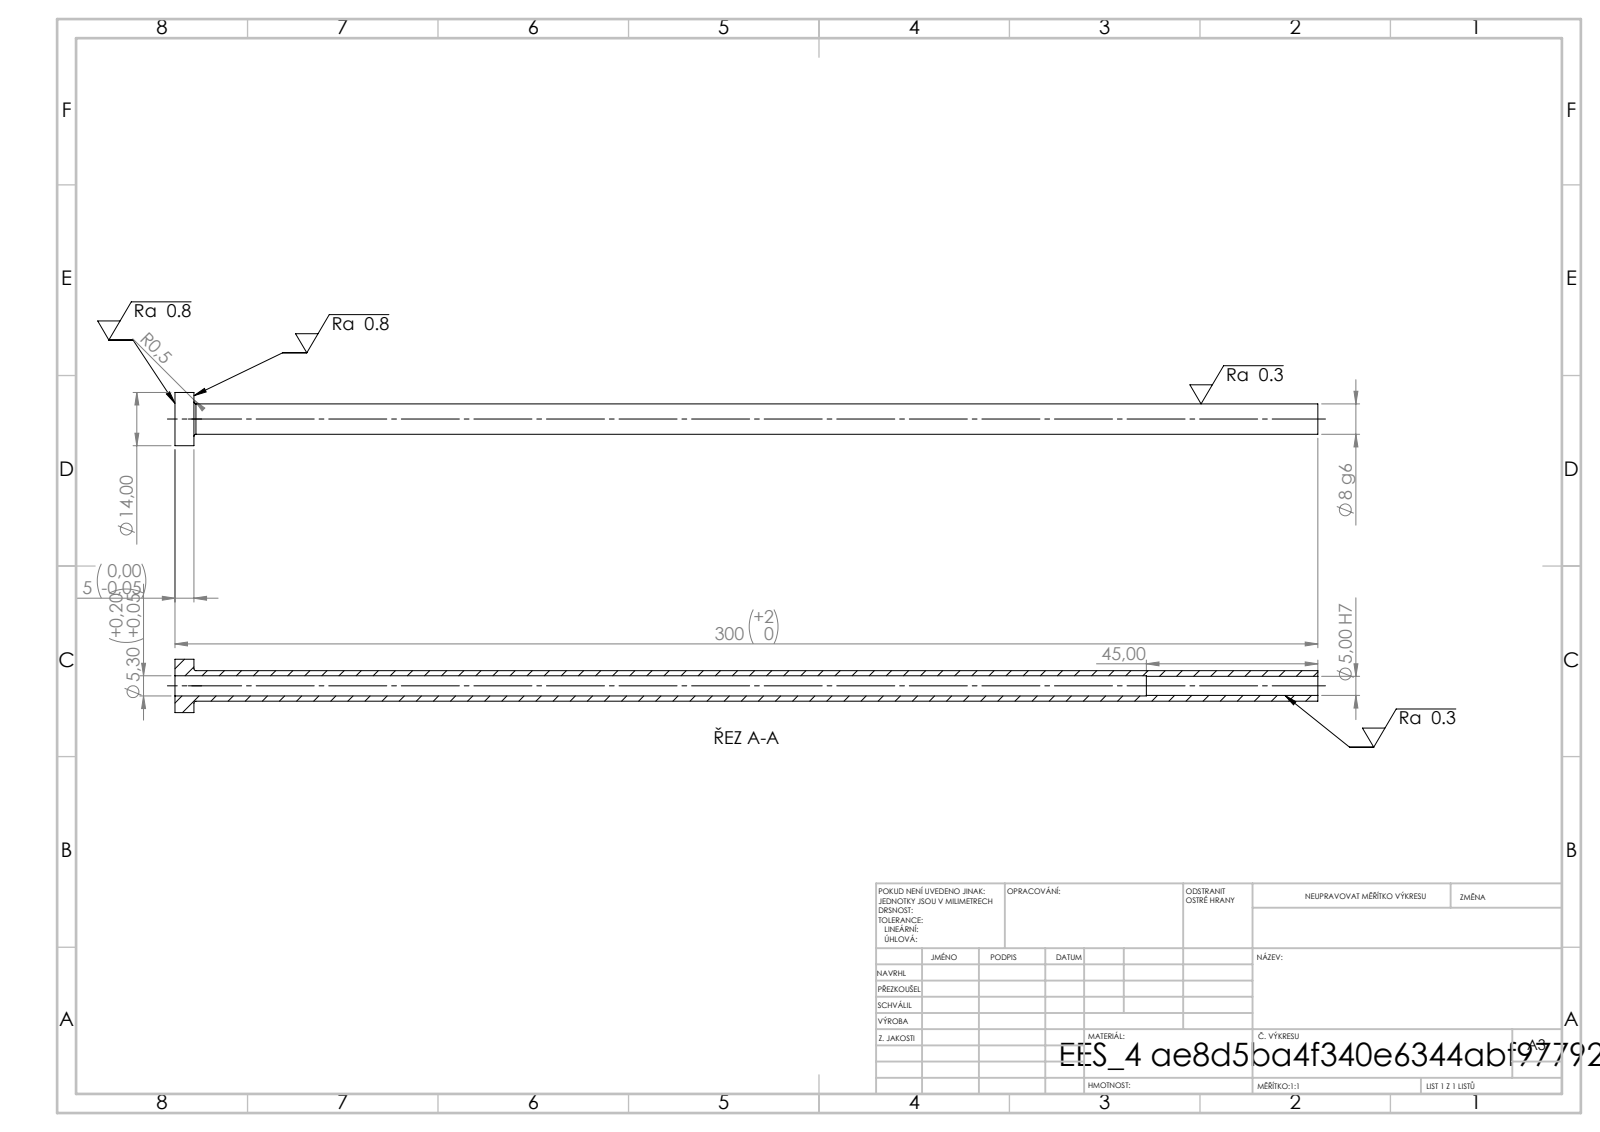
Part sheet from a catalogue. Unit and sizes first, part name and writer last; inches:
Units: inches
Overall size (bounding box): 11.811 × 0.551 × 0.551
Round holes (diameter × count): ⌀0.197 ×1, ⌀0.209 ×1
Round bosses / shafts (diameter × count): ⌀0.551 ×1, ⌀0.315 ×1
Main face-to-face distances: 0.197, 11.811, 11.614, 10.039, 9.843, 1.772
Volume: 0.555 in³ · Surface area: 19.92 in²
Bodies: 1 solid, 14 faces (4 planar, 8 cylindrical, 2 other)
STEP written by: SolidWorks 2019 (CONFIG_CONTROL_DESIGN)
